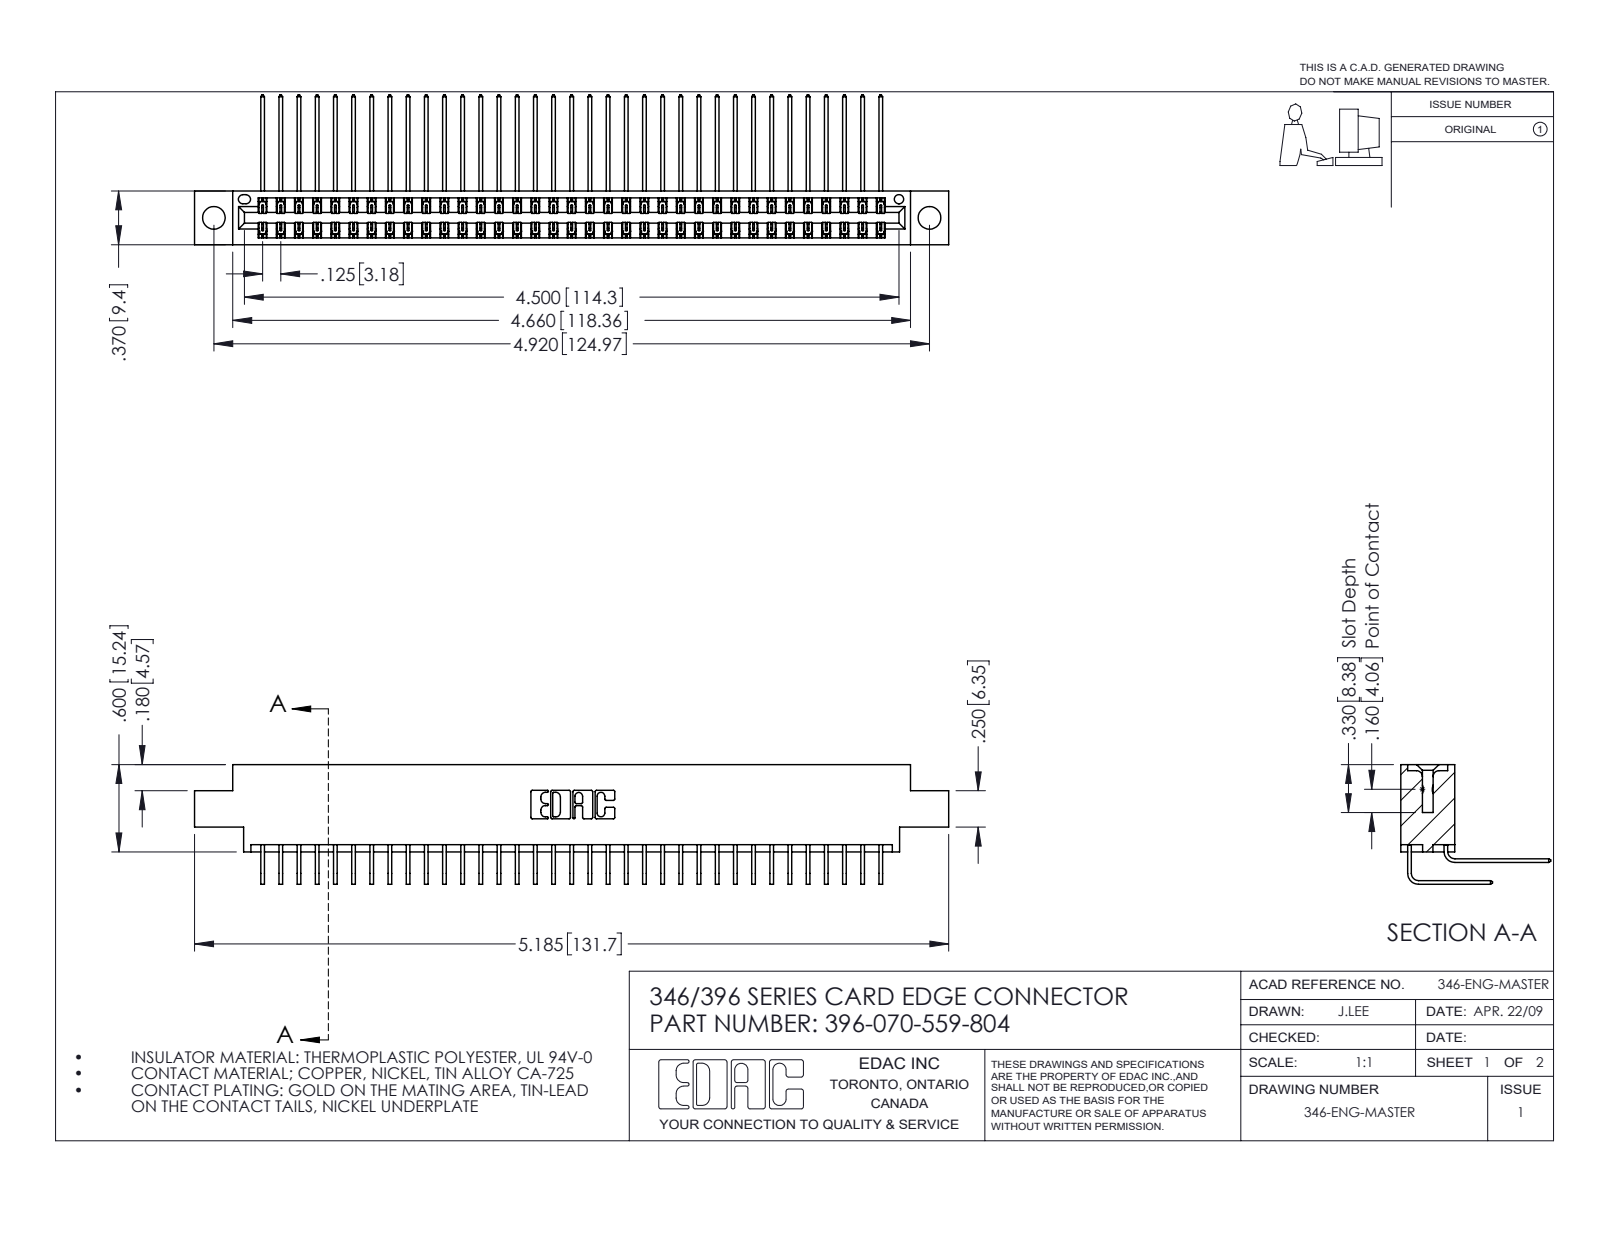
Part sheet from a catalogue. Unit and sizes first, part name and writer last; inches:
Units: inches
Overall size (bounding box): 5.185 × 1.03 × 0.823
Round holes (diameter × count): ⌀0.156 ×2, ⌀0.064 ×1
Partial cylindrical surfaces — rounded edges, fillets, slot ends (radius × count): R0.006 ×105, R0.01 ×22, R0.007 ×6, R0.031 ×6, R0.026 ×3, R0.014 ×2, R0.022 ×2, R0.024 ×2
Main face-to-face distances: 0.048, 0.322, 0.025, 0.37, 0.25, 0.072, 0.298, 0.275, 0.148, 0.222
Hole centre spacings: 0.246, 4.711, 4.92
Volume: 0.79 in³ · Surface area: 30.41 in²
Bodies: 71 solids, 3906 faces (2670 planar, 1236 cylindrical, 0 other)
Part name (STEP PRODUCT): 346 Part_0.170 Offset - 0.156 Dia-TH; 396-070-559-804; 345-292-001_559 Tail - 2; 345-292-001_558 559 Tail - 1
STEP written by: SolidWorks 2016 (CONFIG_CONTROL_DESIGN)
